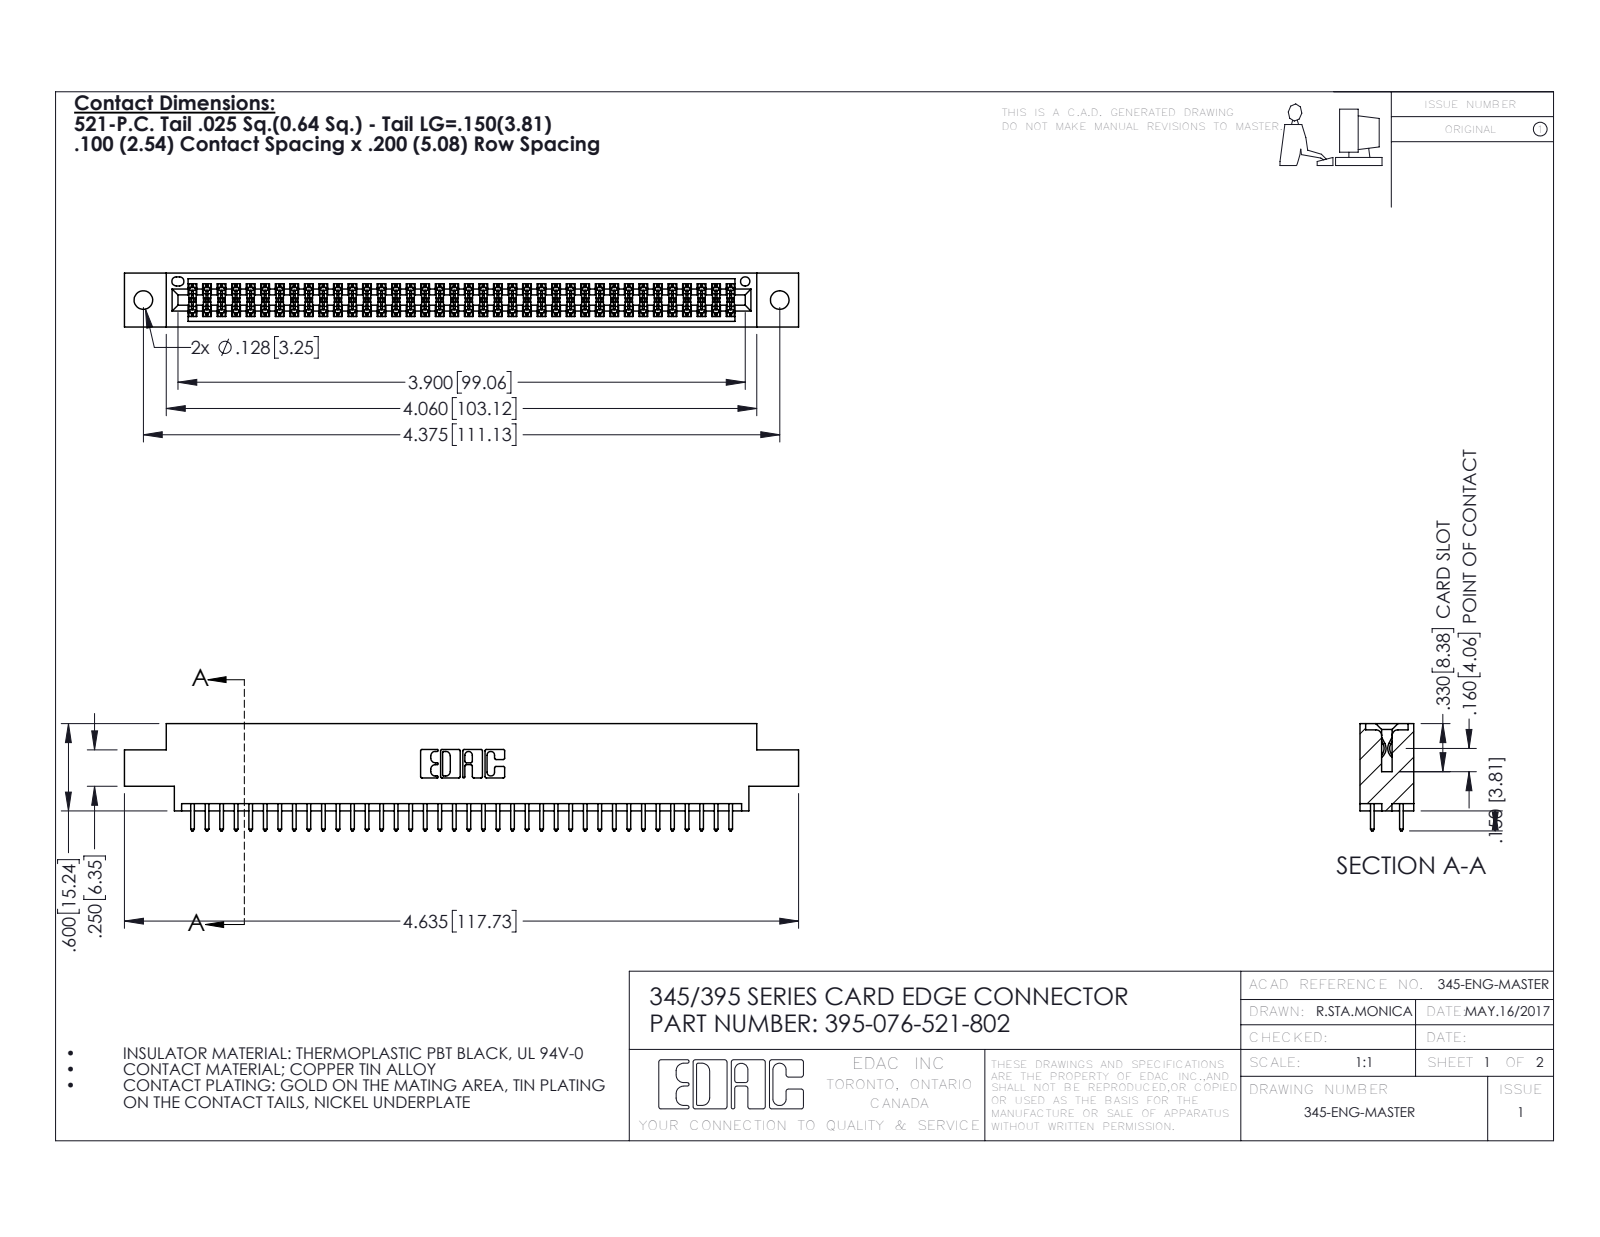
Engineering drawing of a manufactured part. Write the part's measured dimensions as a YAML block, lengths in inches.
part_name: "345-292-001_345-293-121; 345 Part_0.170 Offset - 0.128 Dia; 395-076-521-802"
step_written_by: "SolidWorks 2016 (CONFIG_CONTROL_DESIGN)"
units: inches
bodies: {solids: 77, faces: 3930, planar: 2592, cylindrical: 1338, other: 0}
overall_size: [4.635, 0.737, 0.37]
volume: 0.685
surface_area: 25.07
round_holes:
  - {diameter: 0.128, count: 2}
  - {diameter: 0.064, count: 1}
partial_cylinders:
  - {radius: 0.006, count: 114}
  - {radius: 0.01, count: 76}
  - {radius: 0.01, count: 22}
  - {radius: 0.007, count: 6}
  - {radius: 0.031, count: 6}
  - {radius: 0.026, count: 3}
  - {radius: 0.014, count: 2}
  - {radius: 0.019, count: 2}
face_to_face_distances: [0.298, 0.072, 0.2, 0.37, 0.098, 0.272, 0.025, 0.225, 0.175, 0.149]
hole_center_spacings: [0.27, 4.139, 4.375]
